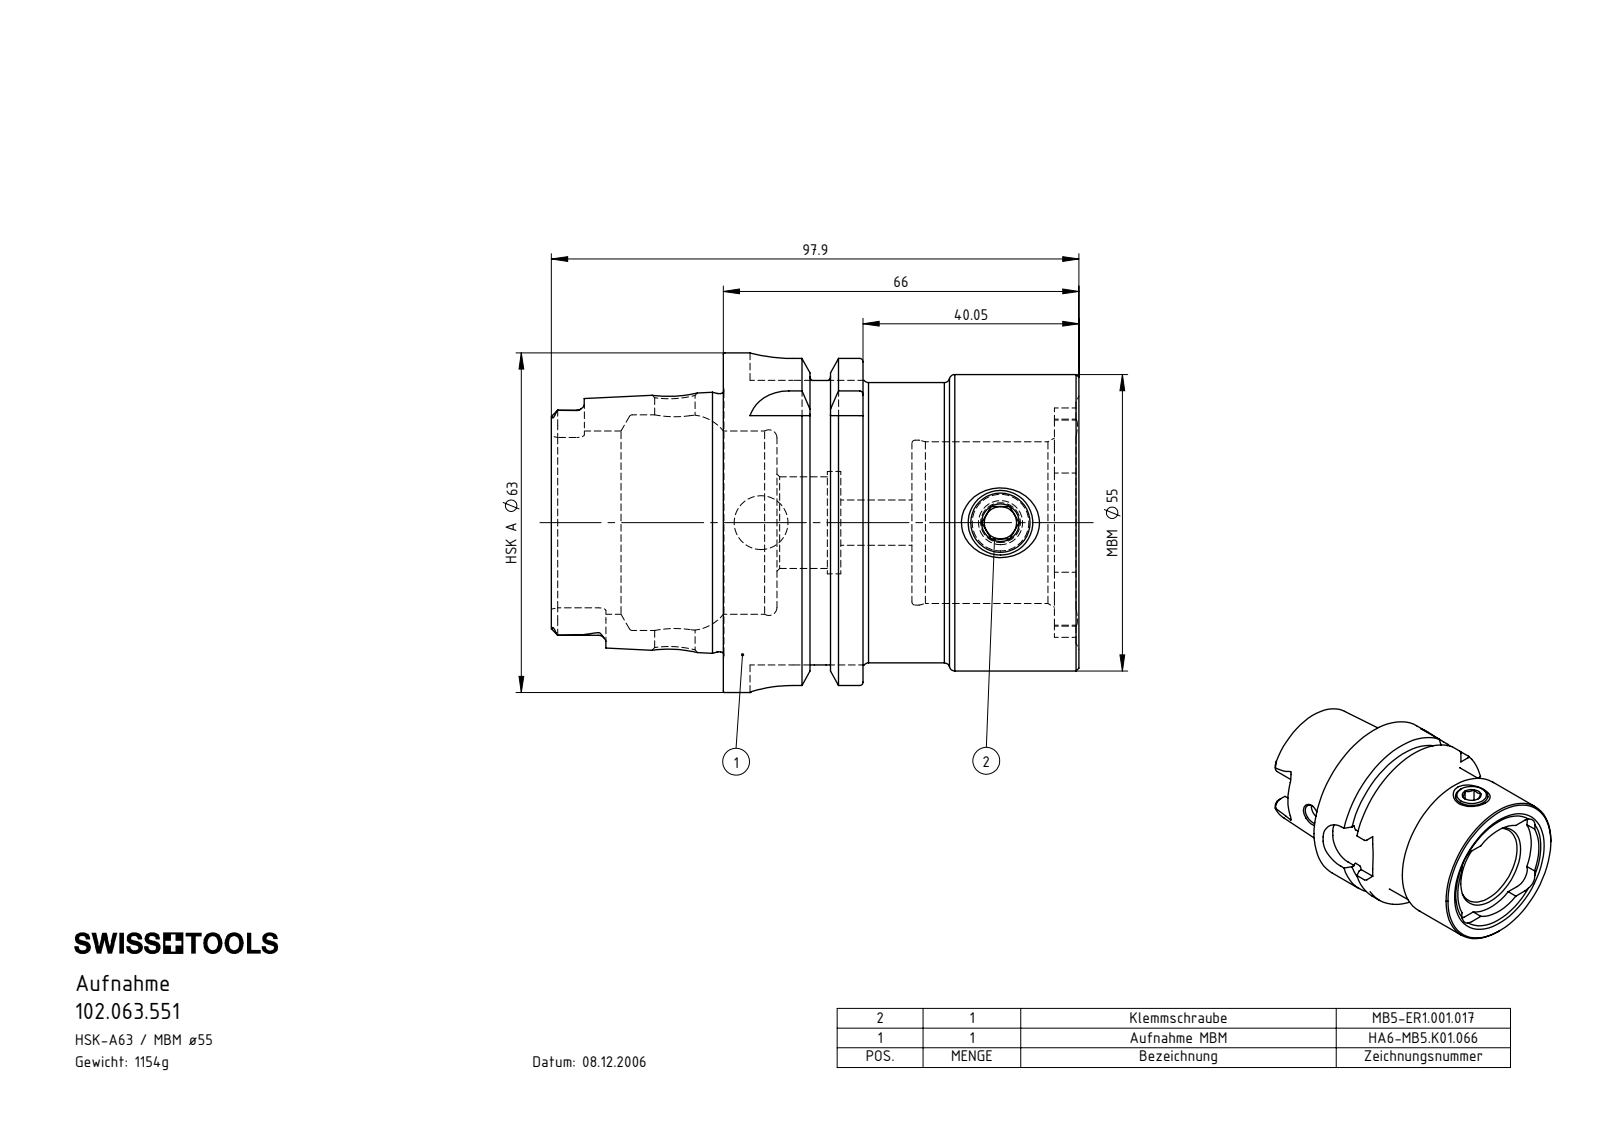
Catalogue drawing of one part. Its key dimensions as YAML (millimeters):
part_name: "HA6-MB5.K01.066_A_Fertigbearbeitung; HA6-MB5.K01.066; MB5-ER1.001.017_A"
step_written_by: "SolidWorks 2012 (CONFIG_CONTROL_DESIGN)"
units: millimeters
bodies: {solids: 2, faces: 220, planar: 65, cylindrical: 66, other: 89}
overall_size: [97.9, 63, 63]
volume: 147130
surface_area: 33625
round_holes:
  - {diameter: 7.5, count: 1}
  - {diameter: 8.4, count: 1}
  - {diameter: 10, count: 1}
  - {diameter: 11, count: 1}
  - {diameter: 17, count: 1}
  - {diameter: 19, count: 1}
  - {diameter: 30, count: 1}
  - {diameter: 30.6, count: 1}
  - {diameter: 34, count: 1}
  - {diameter: 40, count: 1}
round_bosses_or_shafts:
  - {diameter: 63, count: 1}
  - {diameter: 55, count: 1}
  - {diameter: 54.95, count: 1}
  - {diameter: 52, count: 1}
  - {diameter: 47.93, count: 1}
  - {diameter: 12, count: 1}
partial_cylinders:
  - {radius: 1.4, count: 6}
  - {radius: 2.88, count: 4}
  - {radius: 5.2, count: 4}
  - {radius: 8, count: 4}
  - {radius: 18.5, count: 1}
  - {radius: 21.27, count: 1}
face_to_face_distances: [35, 25.05, 35.5, 66, 31, 25.95, 9.05, 40.05, 16, 61.45]
hole_center_spacings: [44.45]
